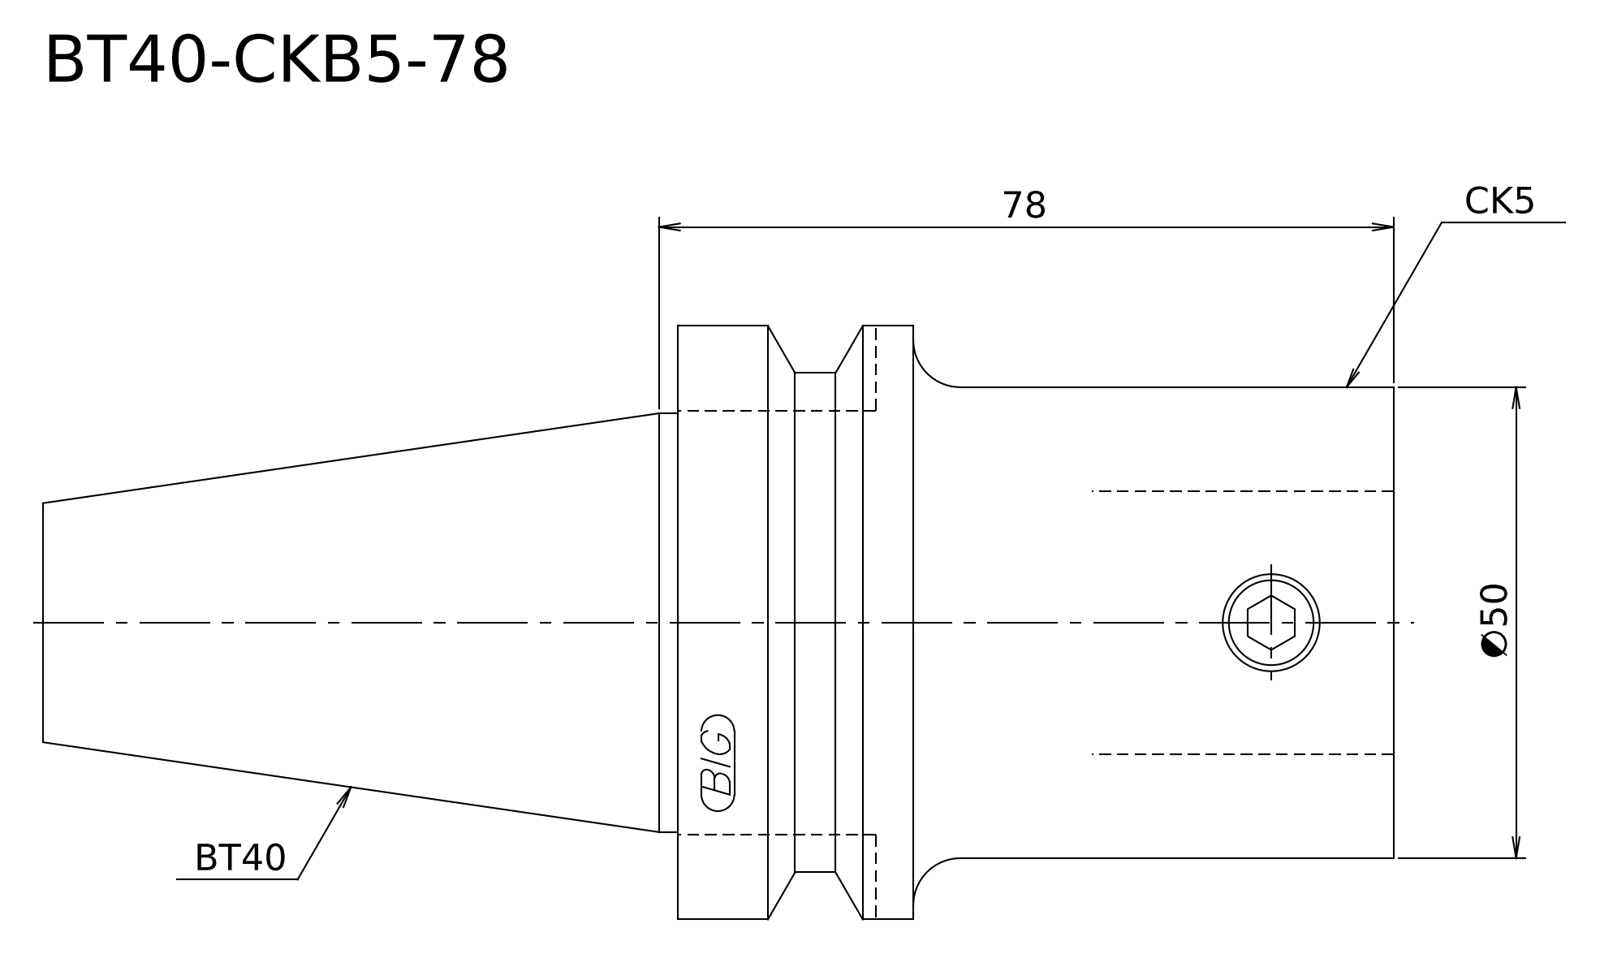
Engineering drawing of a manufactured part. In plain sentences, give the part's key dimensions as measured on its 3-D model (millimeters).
Its 3-D file was written by "Kubotek KeyCreator V8.5.1 (14335) (CONFIG_CONTROL_DESIGN)". It is 1 solid with 14 faces: 4 planar, 5 cylindrical and 5 other. Overall it measures 143.4 by 63 by 63 millimeters. Its volume is 240 589 cubic millimeters and its surface area 26 005 square millimeters. Round bosses or shafts: 1 of diameter 63, 1 of diameter 53, 1 of diameter 50, 1 of diameter 44.45. The main face-to-face distances are 76, 143.4, 67.4, 51, 25, 92.4.
